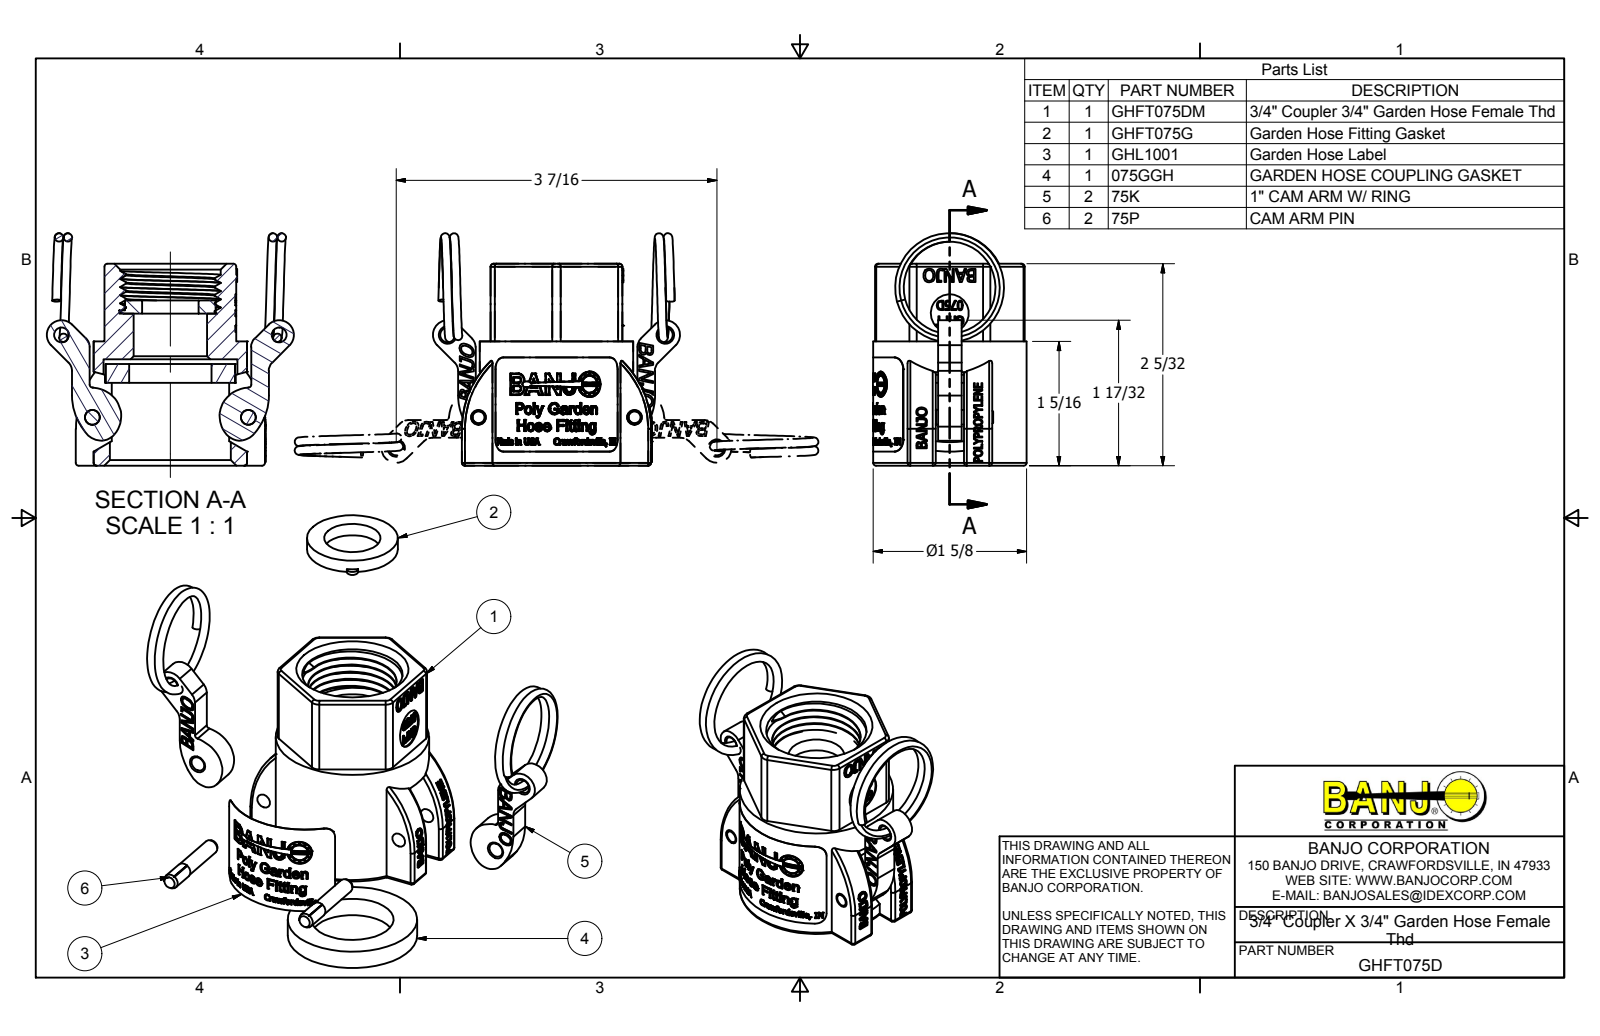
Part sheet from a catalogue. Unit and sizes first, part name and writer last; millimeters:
Units: millimetres
Overall size (bounding box): 66.69 × 62.72 × 41.45
Round holes (diameter × count): ⌀3.96 ×4, ⌀4.04 ×2, ⌀10.16 ×1, ⌀15.24 ×1, ⌀19.81 ×1, ⌀22.22 ×1, ⌀23.89 ×1, ⌀27.13 ×1, ⌀32.61 ×1, ⌀36.12 ×1
Round bosses / shafts (diameter × count): ⌀4.17 ×2, ⌀41.4 ×1, ⌀34.92 ×1, ⌀24.51 ×1
Partial cylindrical surfaces — rounded edges, fillets, slot ends (radius × count): R0.79 ×22, R3.17 ×8, R2.29 ×6, R1.52 ×3, R3.97 ×2, R15.08 ×2, R25.4 ×2, R8.4 ×1
Main face-to-face distances: 6.35, 35.56, 7.62, 15.24, 5.08, 1.27, 18.7, 13.62, 12.35, 22.33
Hole centre spacings: 23.73, 55.1, 42.08, 58.76
Volume: 43 178 mm³ · Surface area: 26 454 mm²
Bodies: 10 solids, 1889 faces (899 planar, 198 cylindrical, 792 other)
Part name (STEP PRODUCT): GHFT075DX; GHFT075DM; GHFT075G; GHL1001 (+7 more)
STEP written by: Autodesk Inventor 2015 (AUTOMOTIVE_DESIGN)
